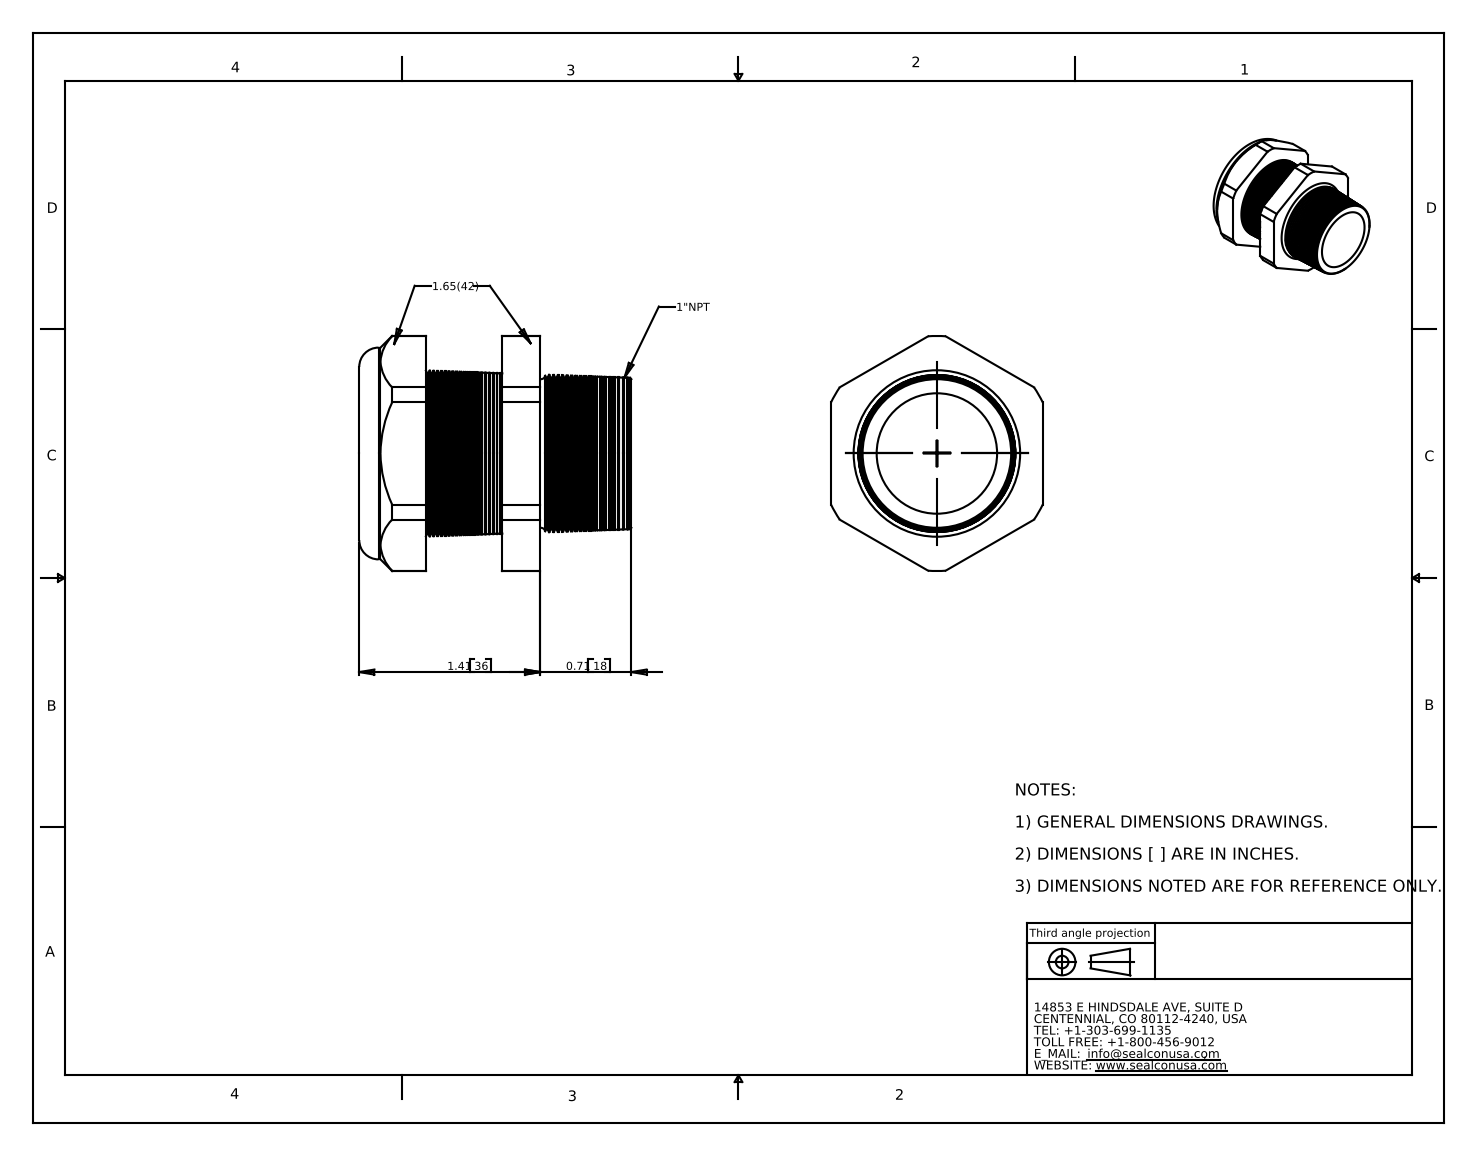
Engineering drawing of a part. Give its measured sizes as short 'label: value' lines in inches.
name: CD29NP-BK
written by: SolidWorks 2007 (CONFIG_CONTROL_DESIGN)
unit: in
bodies: 2 solids, 295 faces (21 planar, 20 cylindrical, 254 other)
size: 2.12 × 1.831 × 1.65
volume: 2.182 in³; area: 26.96 in²
holes: 1× ⌀0.96, 1× ⌀0.98
bosses: 1× ⌀1.65
rounds: 1× R0.916
face distances: 0.595, 0.891, 0.295, 1.65, 0.02, 0.615, 0.91, 0.48, 0.5, 1.095
